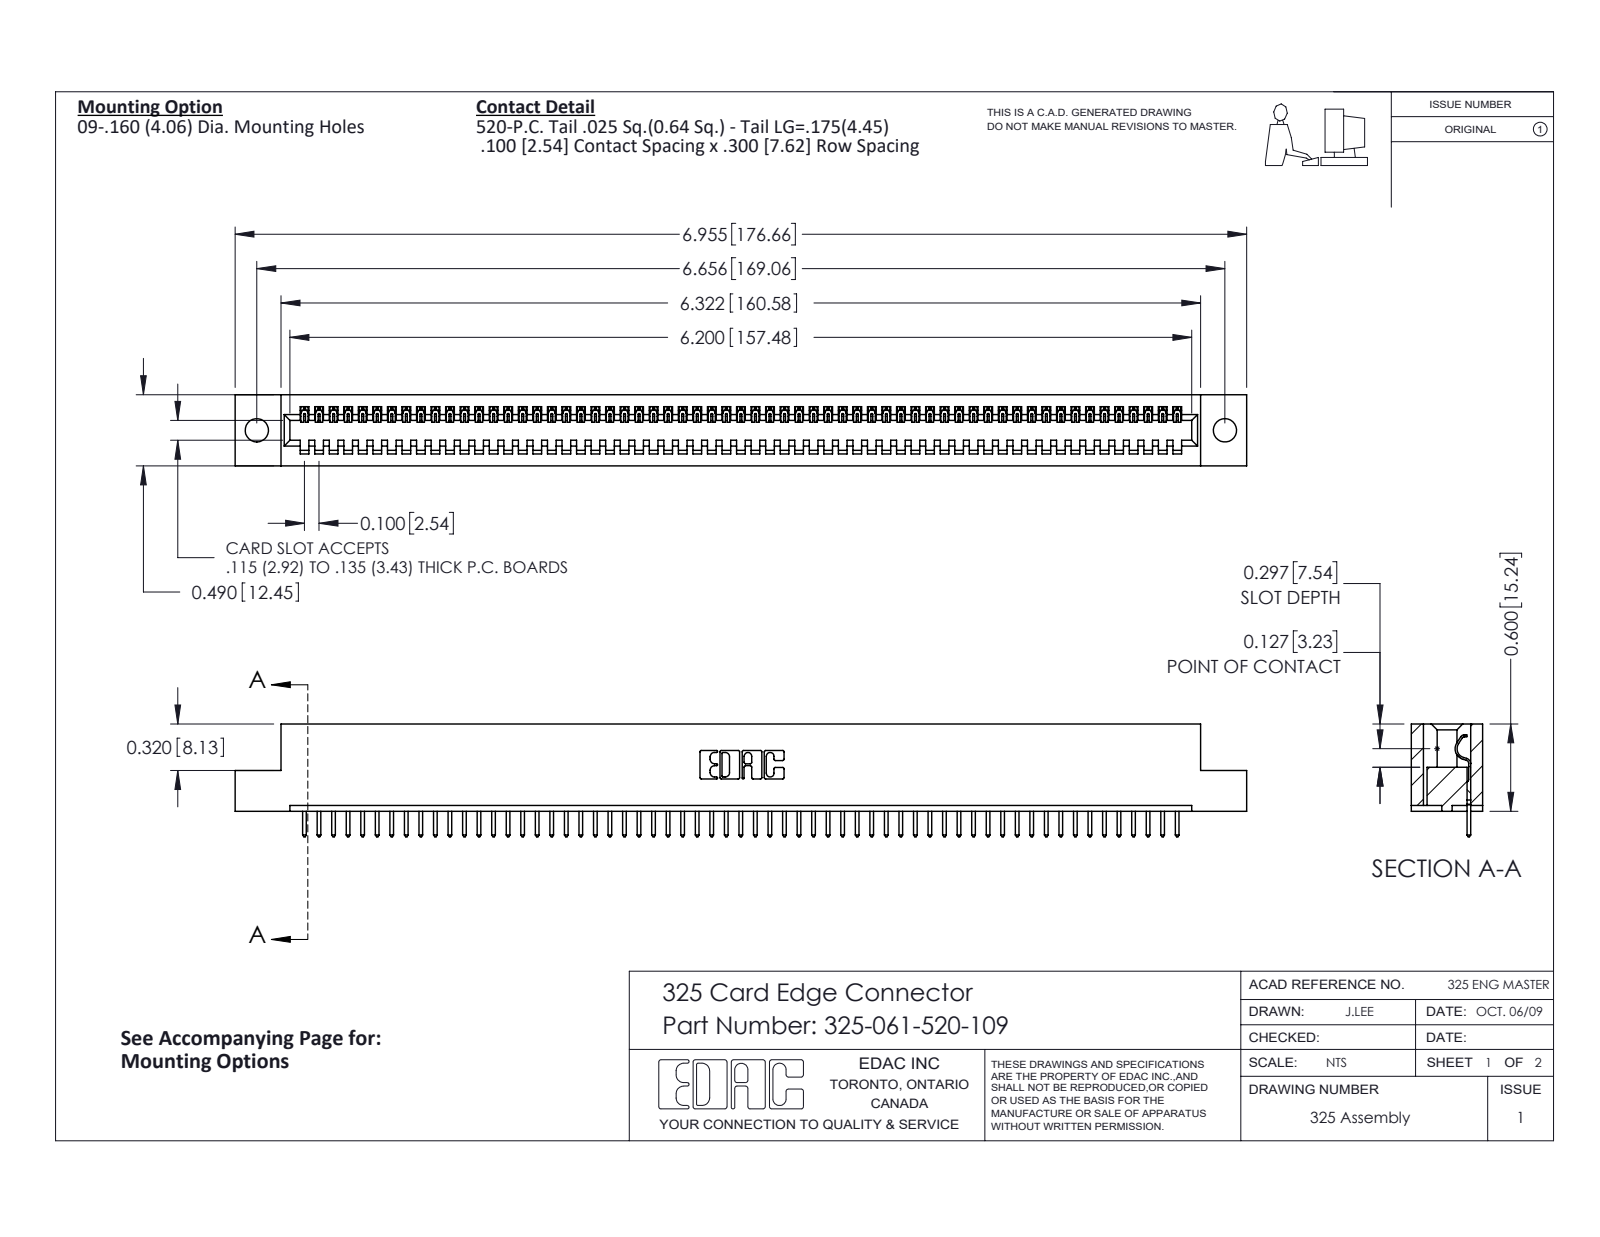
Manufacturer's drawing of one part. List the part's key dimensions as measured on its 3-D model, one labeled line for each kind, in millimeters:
Part name (STEP PRODUCT): 325-292-001_325-293-120; 325-061-520-109; 325 Part_.160 TH
STEP written by: SolidWorks 2016 (CONFIG_CONTROL_DESIGN)
Units: millimetres
Bodies: 62 solids, 3652 faces (2632 planar, 1020 cylindrical, 0 other)
Overall size (bounding box): 176.7 × 19.7 × 12.4
Volume: 22 190 mm³ · Surface area: 23 820 mm²
Round holes (diameter × count): ⌀4.1 ×2
Partial cylindrical surfaces — rounded edges, fillets, slot ends (radius × count): R0.2 ×122, R0.3 ×122, R0.3 ×22, R0.2 ×6, R0.8 ×6, R0.7 ×3, R0.4 ×1, R0.6 ×1
Main face-to-face distances: 2.1, 10.3, 12.4, 2.7, 9.7, 0.6, 7.6, 8.3, 6.7, 14.2
Hole centre spacings: 169.1
